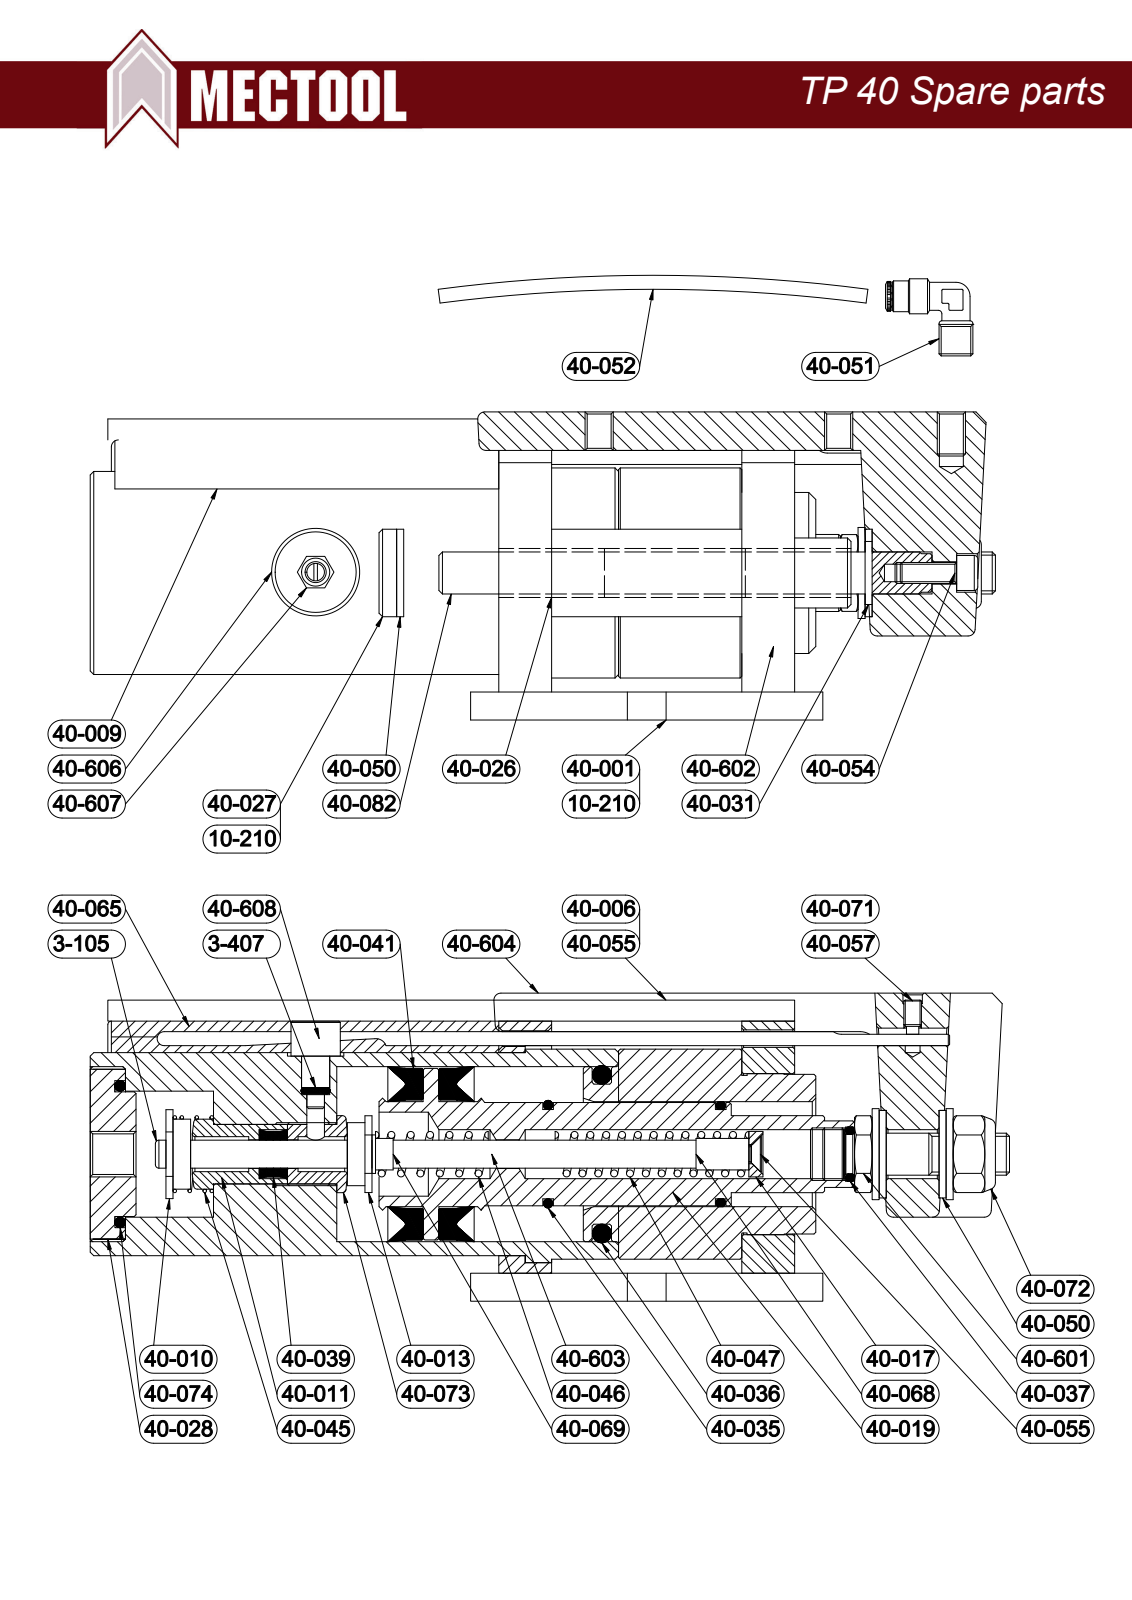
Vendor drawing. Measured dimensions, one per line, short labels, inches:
name: Nut : Standard - M14,0 x 170,434
written by: Spatial InterOp 3D (automotive_design)
unit: in
bodies: 88 solids, 1788 faces (1641 planar, 82 cylindrical, 65 other)
size: 10.157 × 6.299 × 3.504
volume: 80.12 in³; area: 447.3 in²
holes: 10× ⌀0.472, 7× ⌀0.197, 6× ⌀0.266, 2× ⌀0.394, 1× ⌀0.276, 1× ⌀0.315, 1× ⌀0.433, 1× ⌀1.181, 1× ⌀1.969, 1× ⌀2.283
bosses: 3× ⌀0.984, 3× ⌀0.315, 2× ⌀0.787, 2× ⌀0.389, 1× ⌀1.969, 1× ⌀1.811, 1× ⌀1.772, 1× ⌀1.024
rounds: 4× R0.118, 2× R0.217, 1× R0.433
face distances: 0.315, 3.15, 2.717, 2.835, 0.591, 0.236, 3.031, 3.071, 3.386, 3.465
hole spacings: 0.787, 2.717, 2.828, 2.913, 3.622, 3.983, 0.161, 0.474
